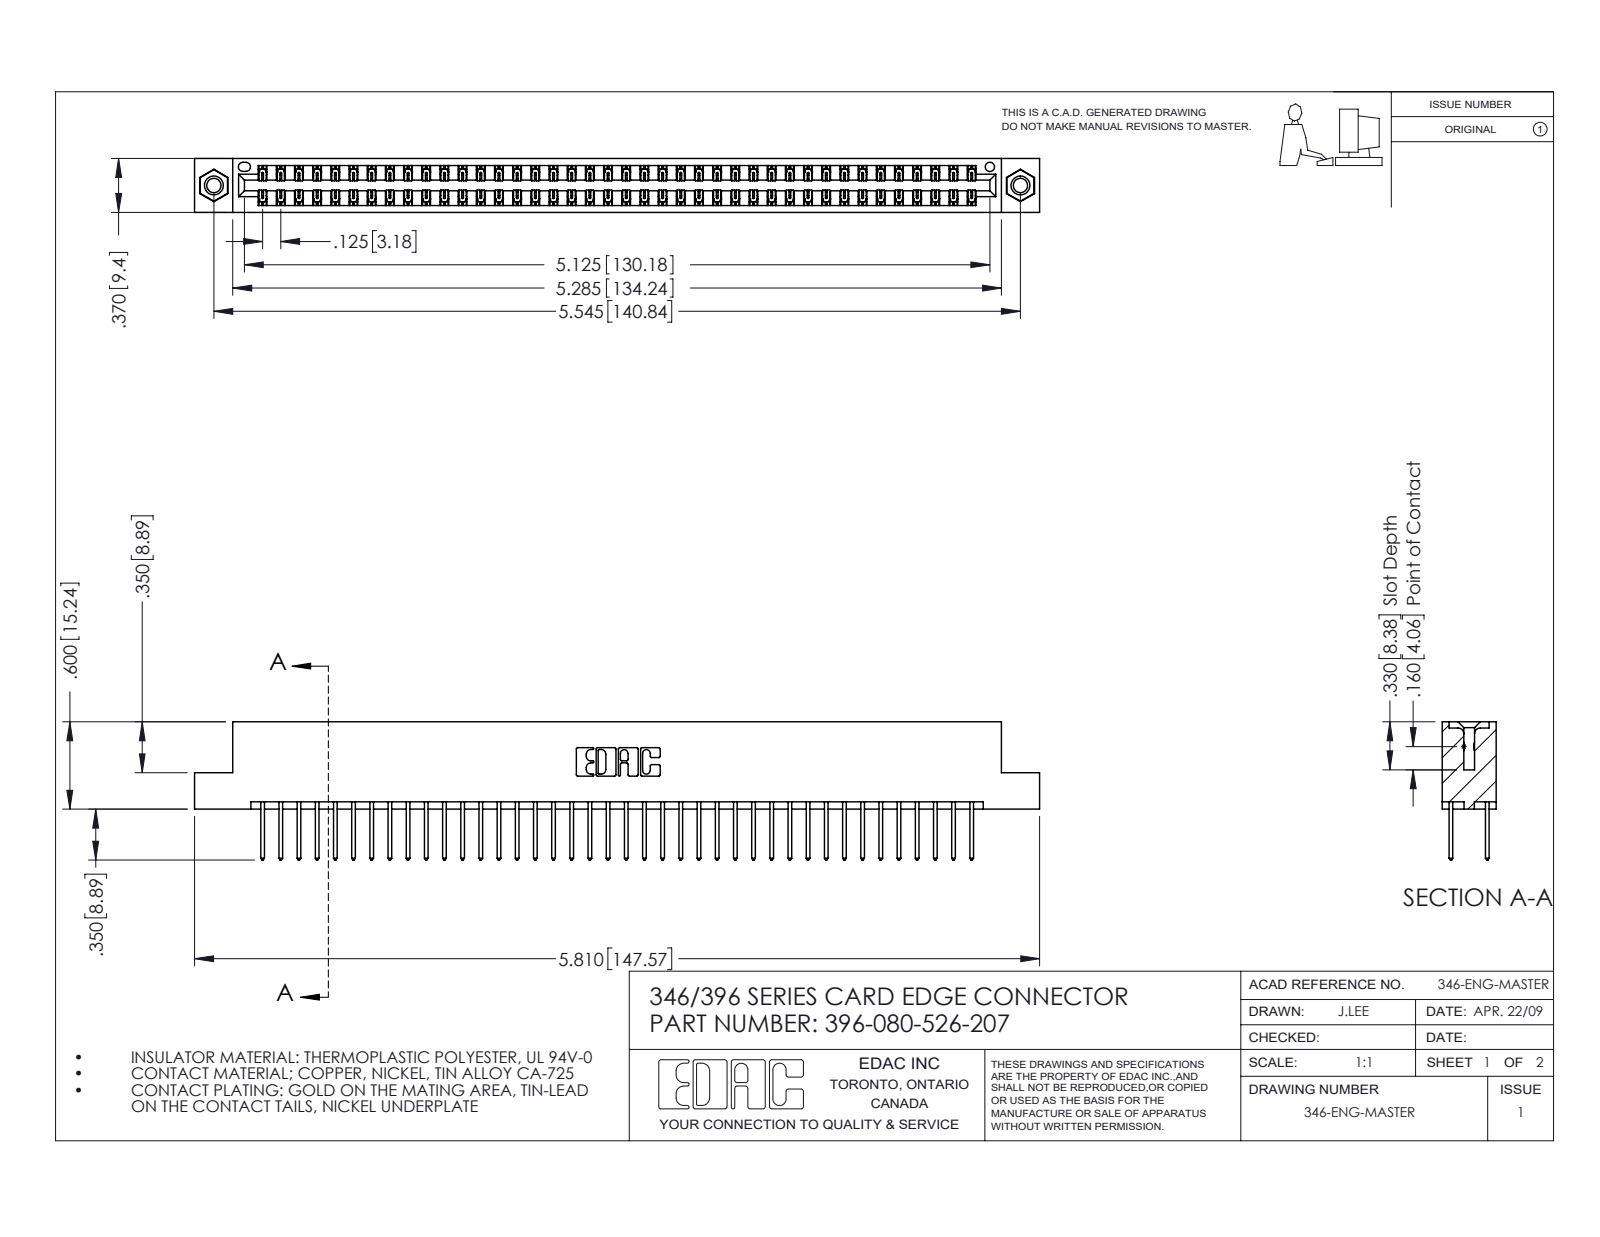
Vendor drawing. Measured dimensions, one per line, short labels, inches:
name: 396-080-526-207; 345-250-001_345-250-005-103; 346 Part_Flush Mounting Lugs - 0.156 Dia-TI; 345-292-001_345-293-126
written by: SolidWorks 2016 (CONFIG_CONTROL_DESIGN)
unit: in
bodies: 83 solids, 4342 faces (2908 planar, 1418 cylindrical, 16 other)
size: 5.81 × 0.95 × 0.37
volume: 0.884 in³; area: 31.79 in²
holes: 2× ⌀0.098, 2× ⌀0.125, 2× ⌀0.156, 1× ⌀0.064
bosses: 2× ⌀0.155
rounds: 120× R0.006, 80× R0.01, 22× R0.01, 6× R0.007, 6× R0.031, 3× R0.026, 2× R0.014, 2× R0.022
face distances: 0.048, 0.322, 0.25, 0.37, 0.072, 0.298, 0.025, 0.275, 0.148, 0.222
hole spacings: 0.246, 5.336, 5.545
